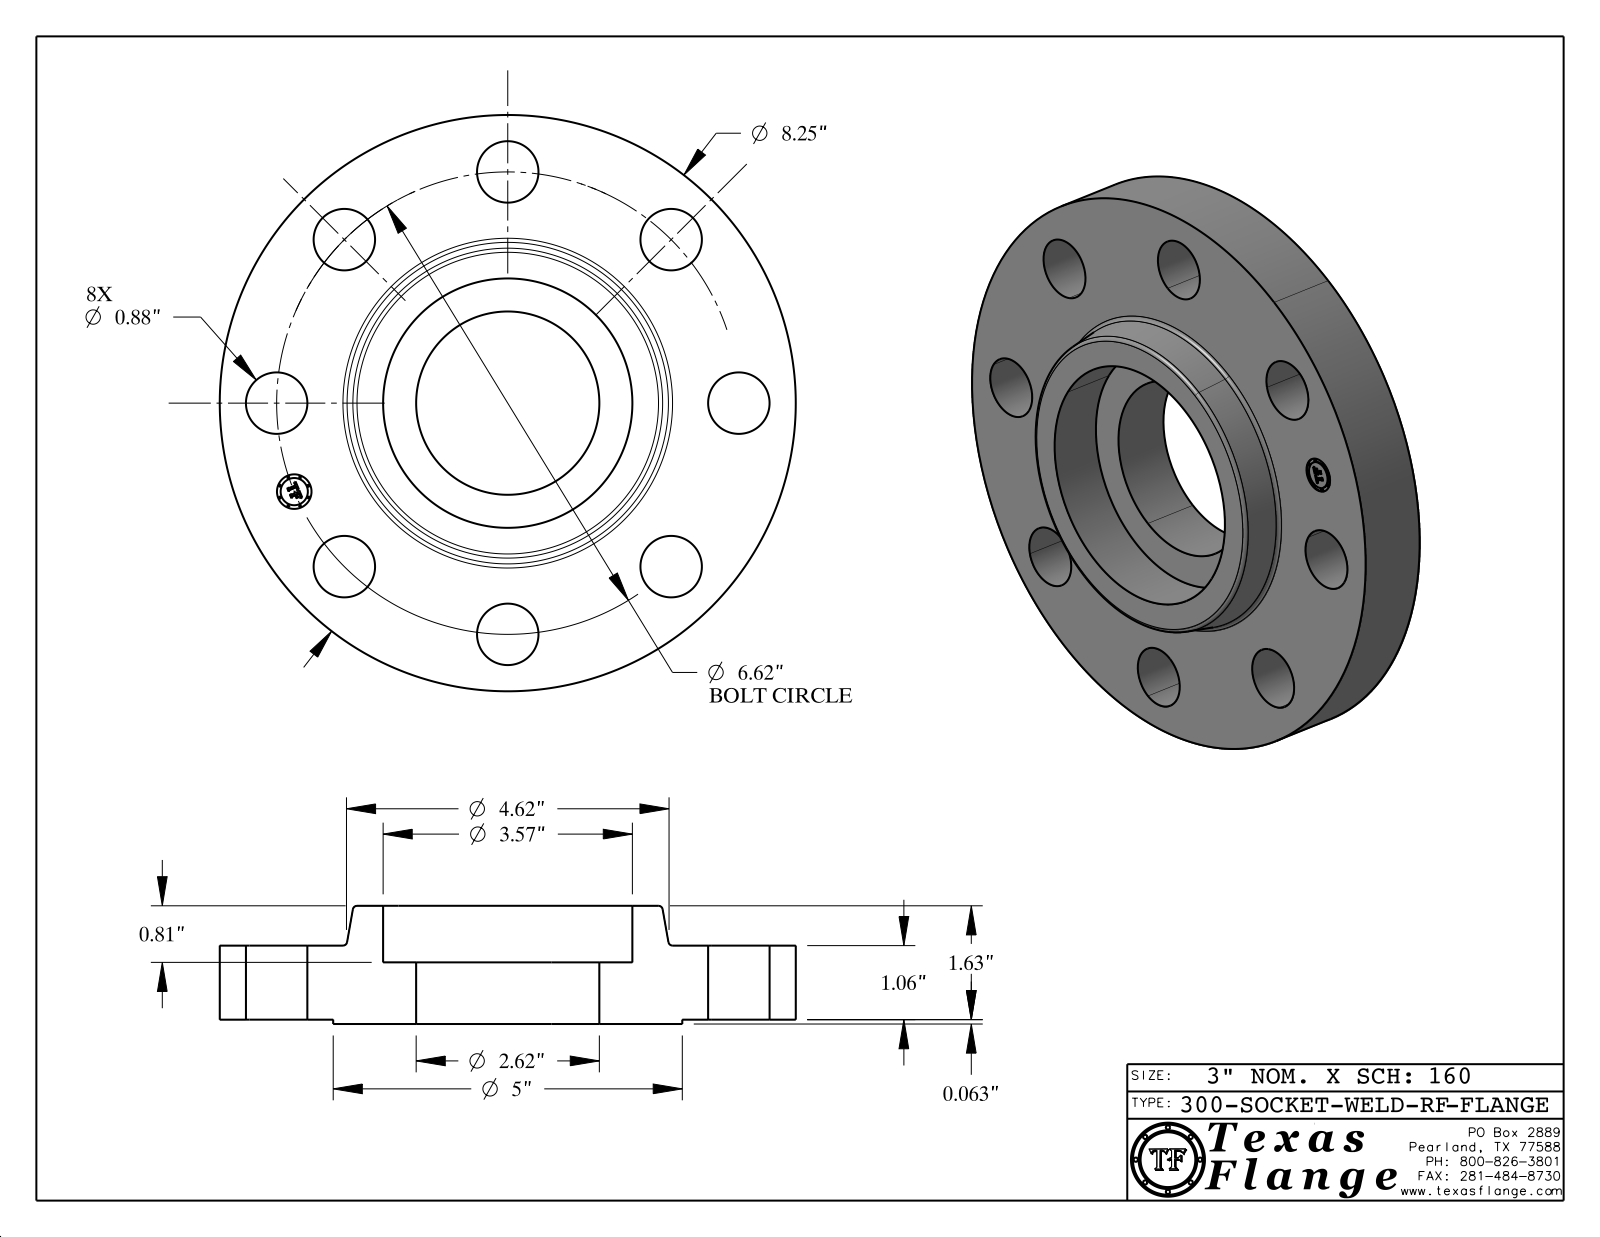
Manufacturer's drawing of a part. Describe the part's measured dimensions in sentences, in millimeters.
The part is named "300-SOCKET-WELD-RF". Its 3-D file was written by "CATIA V5 STEP AP214 (AUTOMOTIVE_DESIGN)". It is 1 solid with 420 faces: 370 planar, 44 cylindrical and 6 other. Overall it measures 209.6 by 209.6 by 43 millimeters. Its volume is 803 000 cubic millimeters and its surface area 103 900 square millimeters. Round holes: 8 of diameter 22.4, 1 of diameter 12.6, 1 of diameter 66.6, 1 of diameter 90.7. Round bosses or shafts: 8 of diameter 0.8, 1 of diameter 209.6, 1 of diameter 127, 1 of diameter 9.9. The main face-to-face distances are 26.9, 1.6, 28.5, 43, 41.4, 14.5, 22.4, 20.8, 6.1, 20.6. The hole center spacings are 84.1, 64.3, 155.3, 118.9, 118.9, 32.8, 93.4, 164.9.
